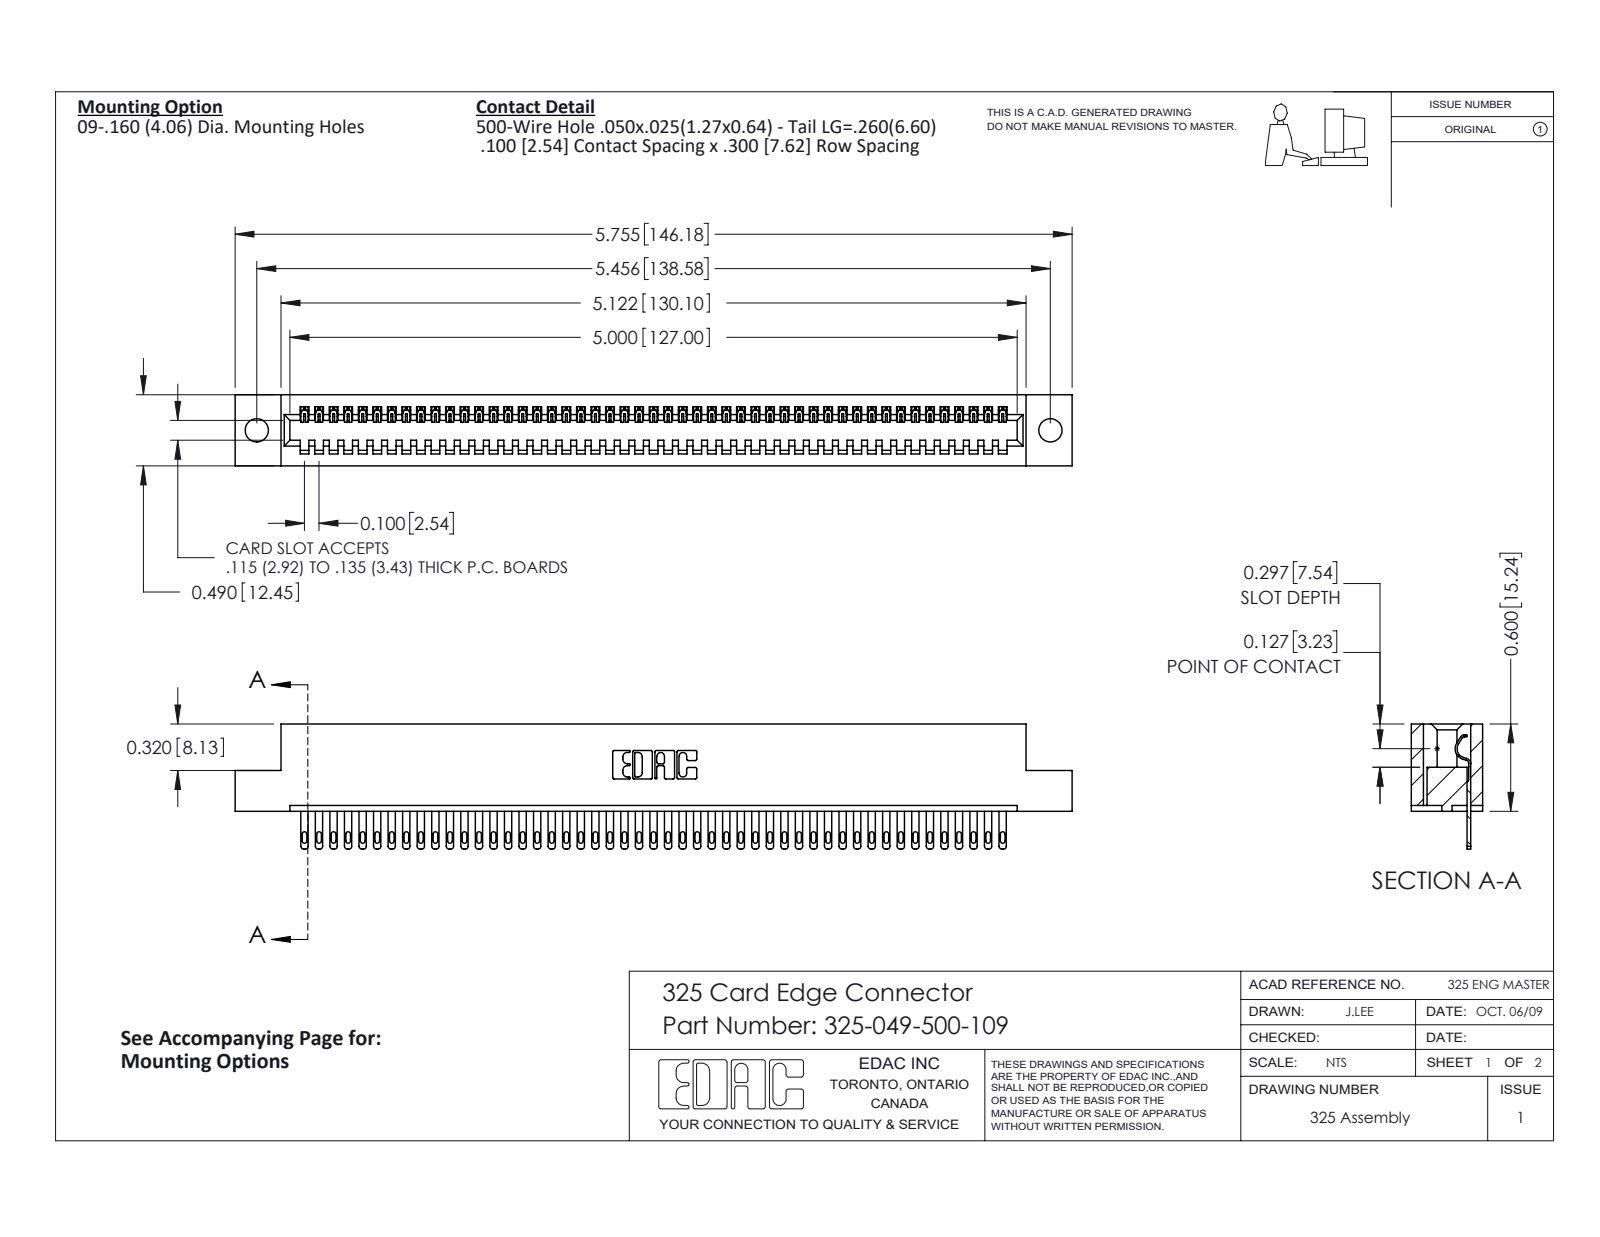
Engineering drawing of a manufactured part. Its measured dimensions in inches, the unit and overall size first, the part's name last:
Units: inches
Overall size (bounding box): 5.755 × 0.86 × 0.49
Round holes (diameter × count): ⌀0.16 ×2
Partial cylindrical surfaces — rounded edges, fillets, slot ends (radius × count): R0.006 ×98, R0.016 ×98, R0.02 ×98, R0.01 ×22, R0.007 ×6, R0.031 ×6, R0.026 ×3, R0.014 ×1
Main face-to-face distances: 0.083, 0.407, 0.49, 0.3, 0.107, 0.383, 0.025, 0.325, 0.56, 0.263
Hole centre spacings: 5.456
Volume: 1.124 in³ · Surface area: 31.38 in²
Bodies: 50 solids, 2760 faces (1834 planar, 926 cylindrical, 0 other)
Part name (STEP PRODUCT): 325-049-500-109; 325 Part_.160 TH; 325-292-001_325-293-100
STEP written by: SolidWorks 2016 (CONFIG_CONTROL_DESIGN)
